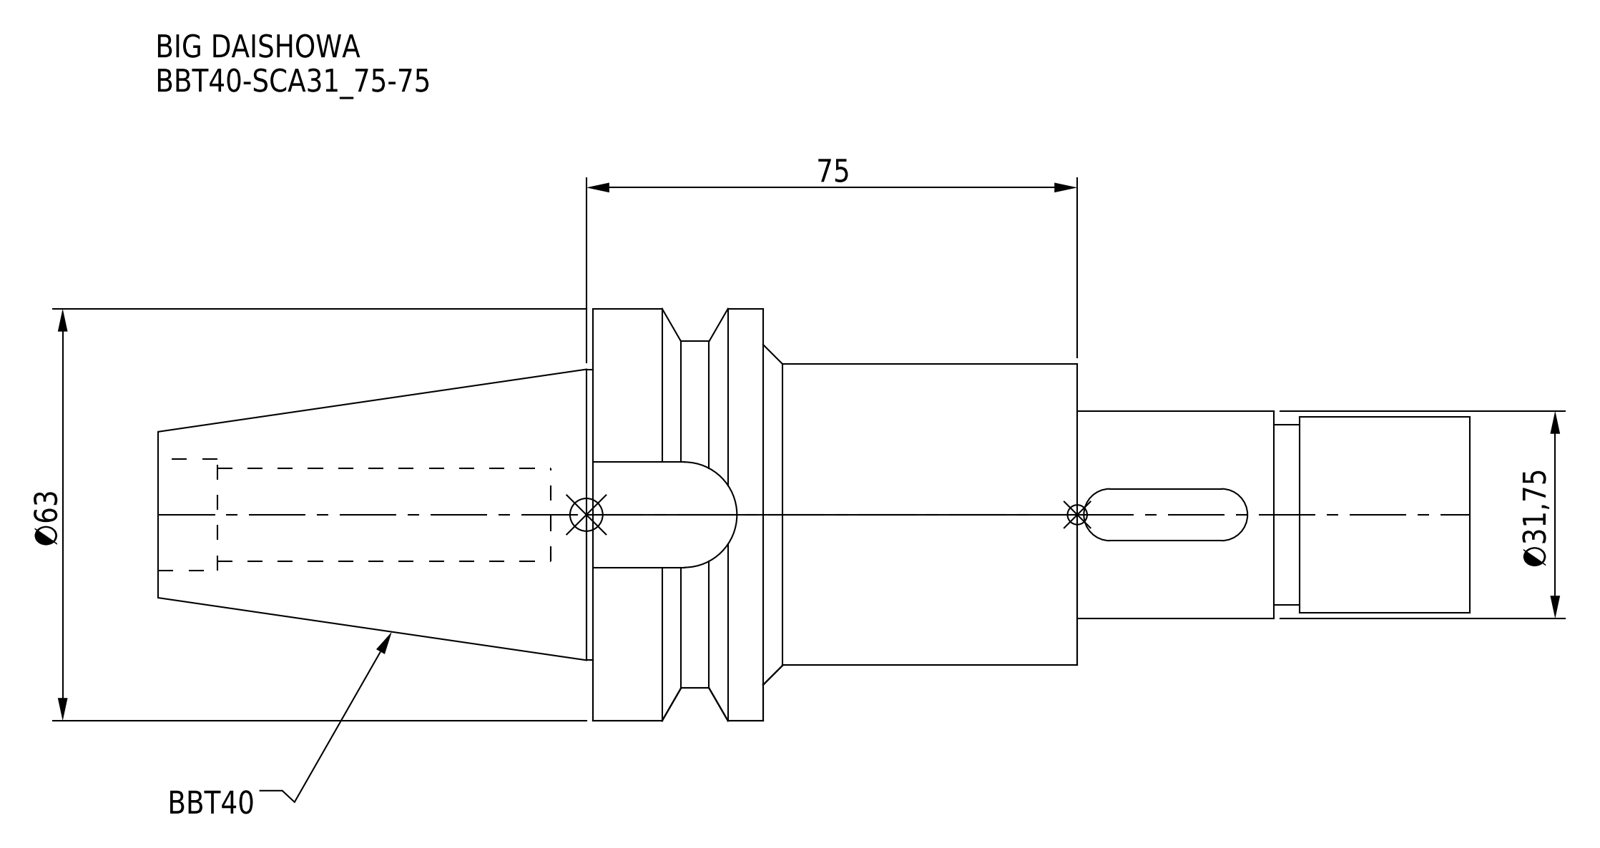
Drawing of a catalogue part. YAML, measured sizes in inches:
part_name: "BBT40-SCA31_75-75"
step_written_by: "CREO PARAMETRIC BY PTC INC, 2016380 (AUTOMOTIVE_DESIGN)"
units: inches
bodies: {solids: 1, faces: 50, planar: 18, cylindrical: 24, other: 8}
overall_size: [7.89, 2.48, 2.48]
volume: 15.32
surface_area: 53.43
round_holes:
  - {diameter: 0.559, count: 1}
  - {diameter: 0.669, count: 1}
round_bosses_or_shafts:
  - {diameter: 2.48, count: 1}
  - {diameter: 2.087, count: 1}
  - {diameter: 1.811, count: 1}
  - {diameter: 1.75, count: 1}
  - {diameter: 1.25, count: 1}
  - {diameter: 1.181, count: 1}
  - {diameter: 1.083, count: 1}
partial_cylinders:
  - {radius: 0.156, count: 2}
  - {radius: 0.317, count: 1}
face_to_face_distances: [1.024, 1.89, 2.913, 2.362, 4.252, 5.276, 5.528, 1.181, 1.772, 7.89]
